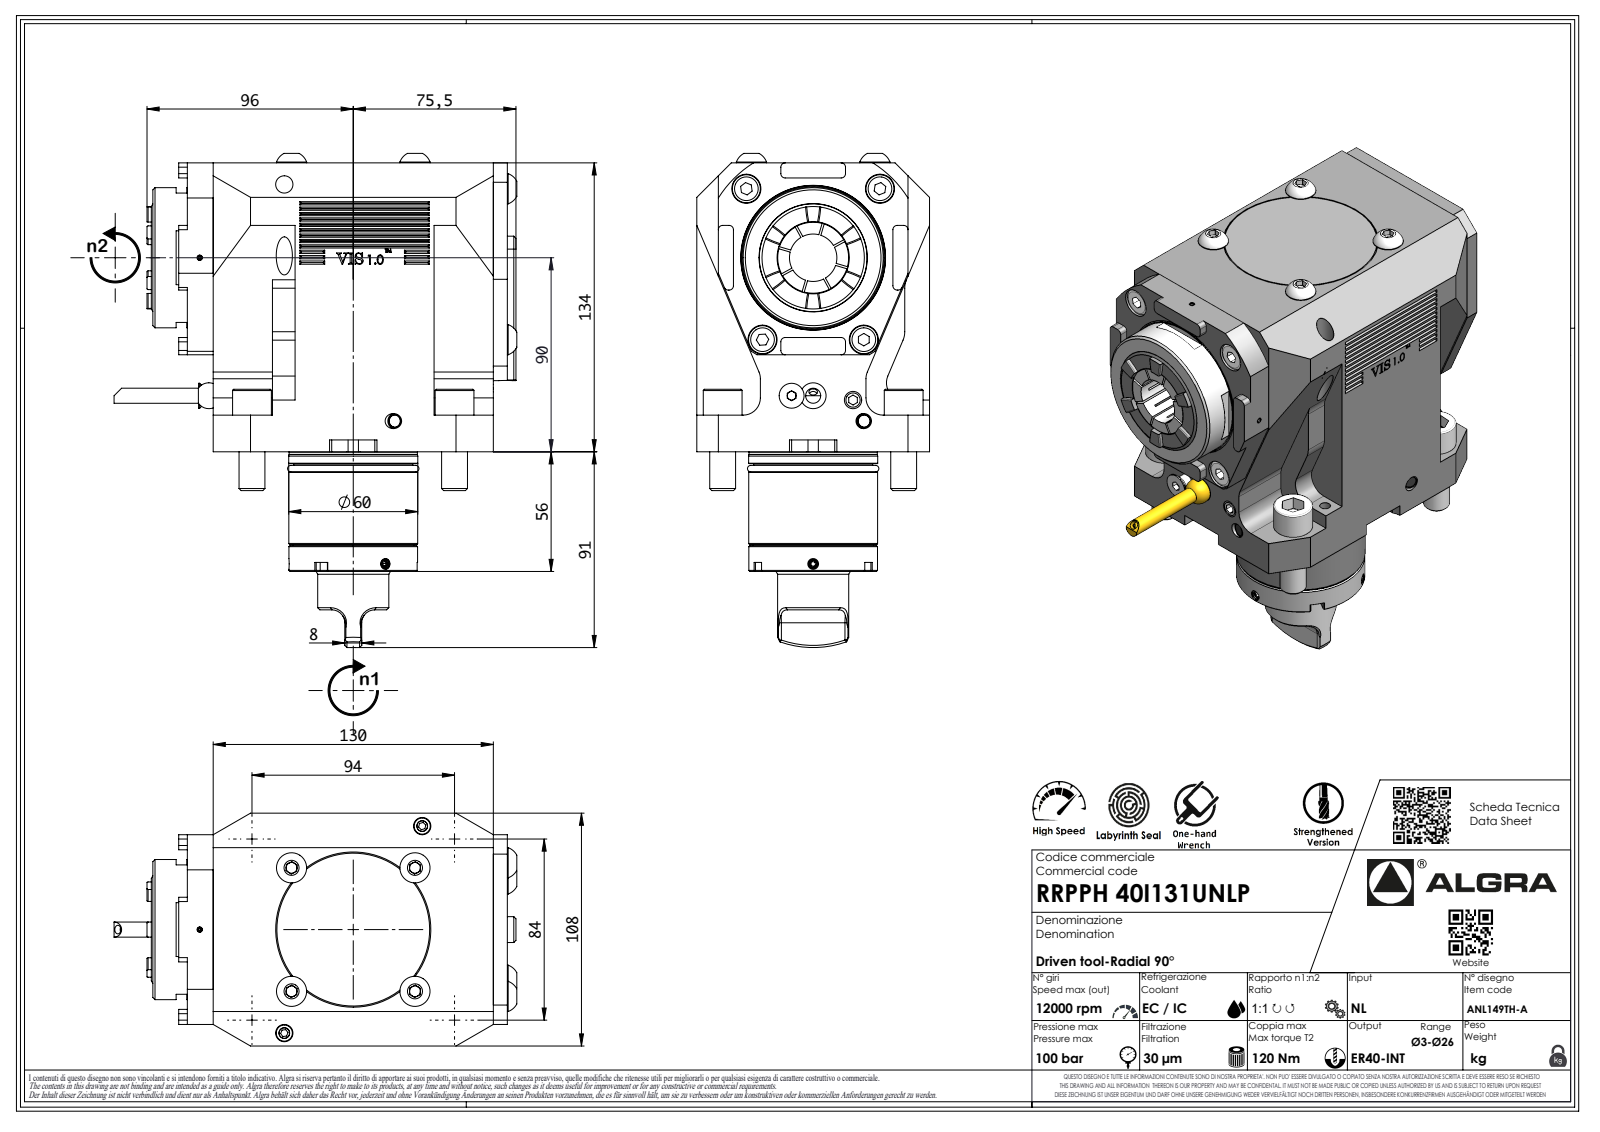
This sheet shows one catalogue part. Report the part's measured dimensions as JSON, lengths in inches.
{"part_name": "RRPPH40I131UNLP", "step_written_by": "SolidWorks 2023 (AUTOMOTIVE_DESIGN)", "units": "inches", "bodies": {"solids": 1, "faces": 962, "planar": 655, "cylindrical": 128, "other": 179}, "overall_size": [8.85, 7.343, 4.252], "volume_in3": 124.2, "surface_area_in2": 196.5, "round_holes": [[0.083, 1], [0.157, 1]], "round_bosses_or_shafts": [[0.709, 4], [0.472, 4], [2.559, 1], [2.358, 1], [2.354, 1], [2.35, 1], [2.343, 1], [2.173, 1]], "partial_cylinders_radius": [[0.008, 21], [0.315, 18], [0.079, 16], [0.236, 11], [0.013, 7], [0.02, 7], [0.146, 7], [0.394, 4]], "face_to_face_distances": [4.252, 5.276, 0.472, 1.083, 0.63, 4.035, 1.102, 2.185, 0.256, 5.374]}
